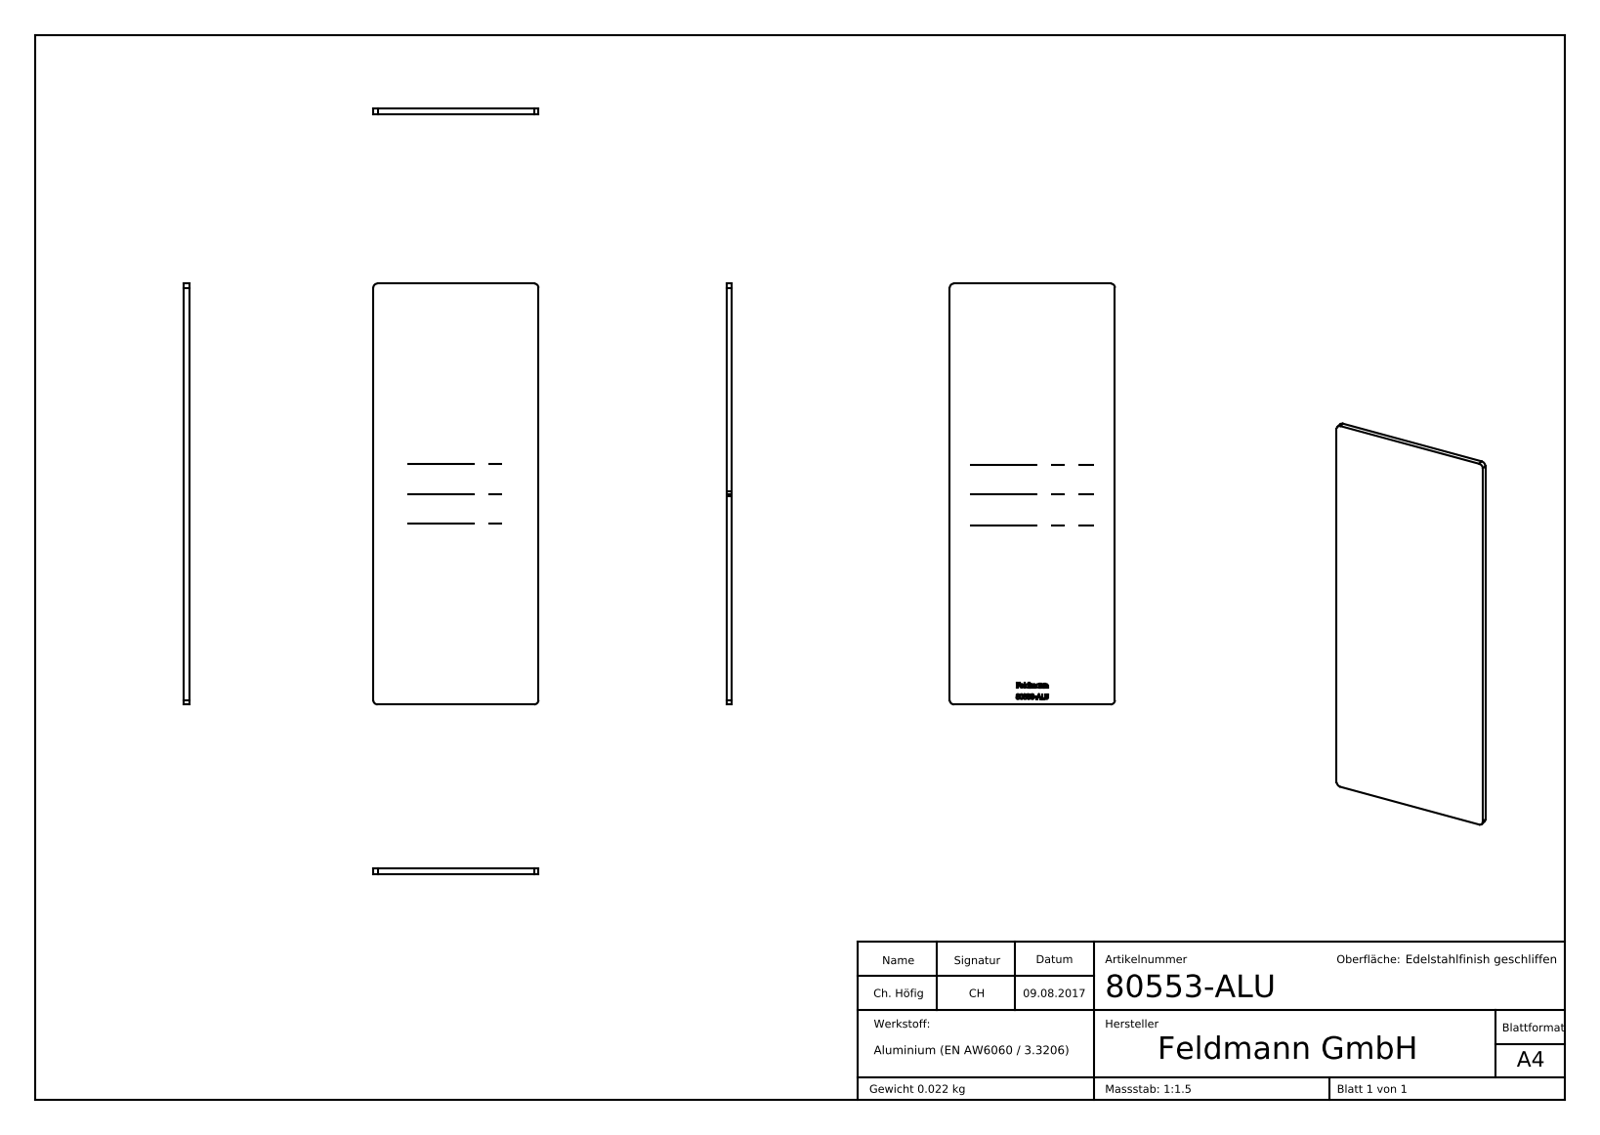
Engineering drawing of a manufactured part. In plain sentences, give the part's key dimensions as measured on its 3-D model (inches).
The part is named "80553-ALU". Its 3-D file was written by "SolidWorks 2015 (CONFIG_CONTROL_DESIGN)". It is 1 solid with 241 faces: 126 planar, 4 cylindrical and 111 other. Overall it measures 4.665 by 1.831 by 0.059 inches. Its volume is 0.504 cubic inches and its surface area 17.86 square inches. Partial cylindrical surfaces (rounded edges, fillets, slot ends): 4 of radius 0.047. The main face-to-face distances are 0.059, 1.831, 4.665, 0.055, 0.146, 0.144, 0.275, 0.129, 0.08, 0.029.
